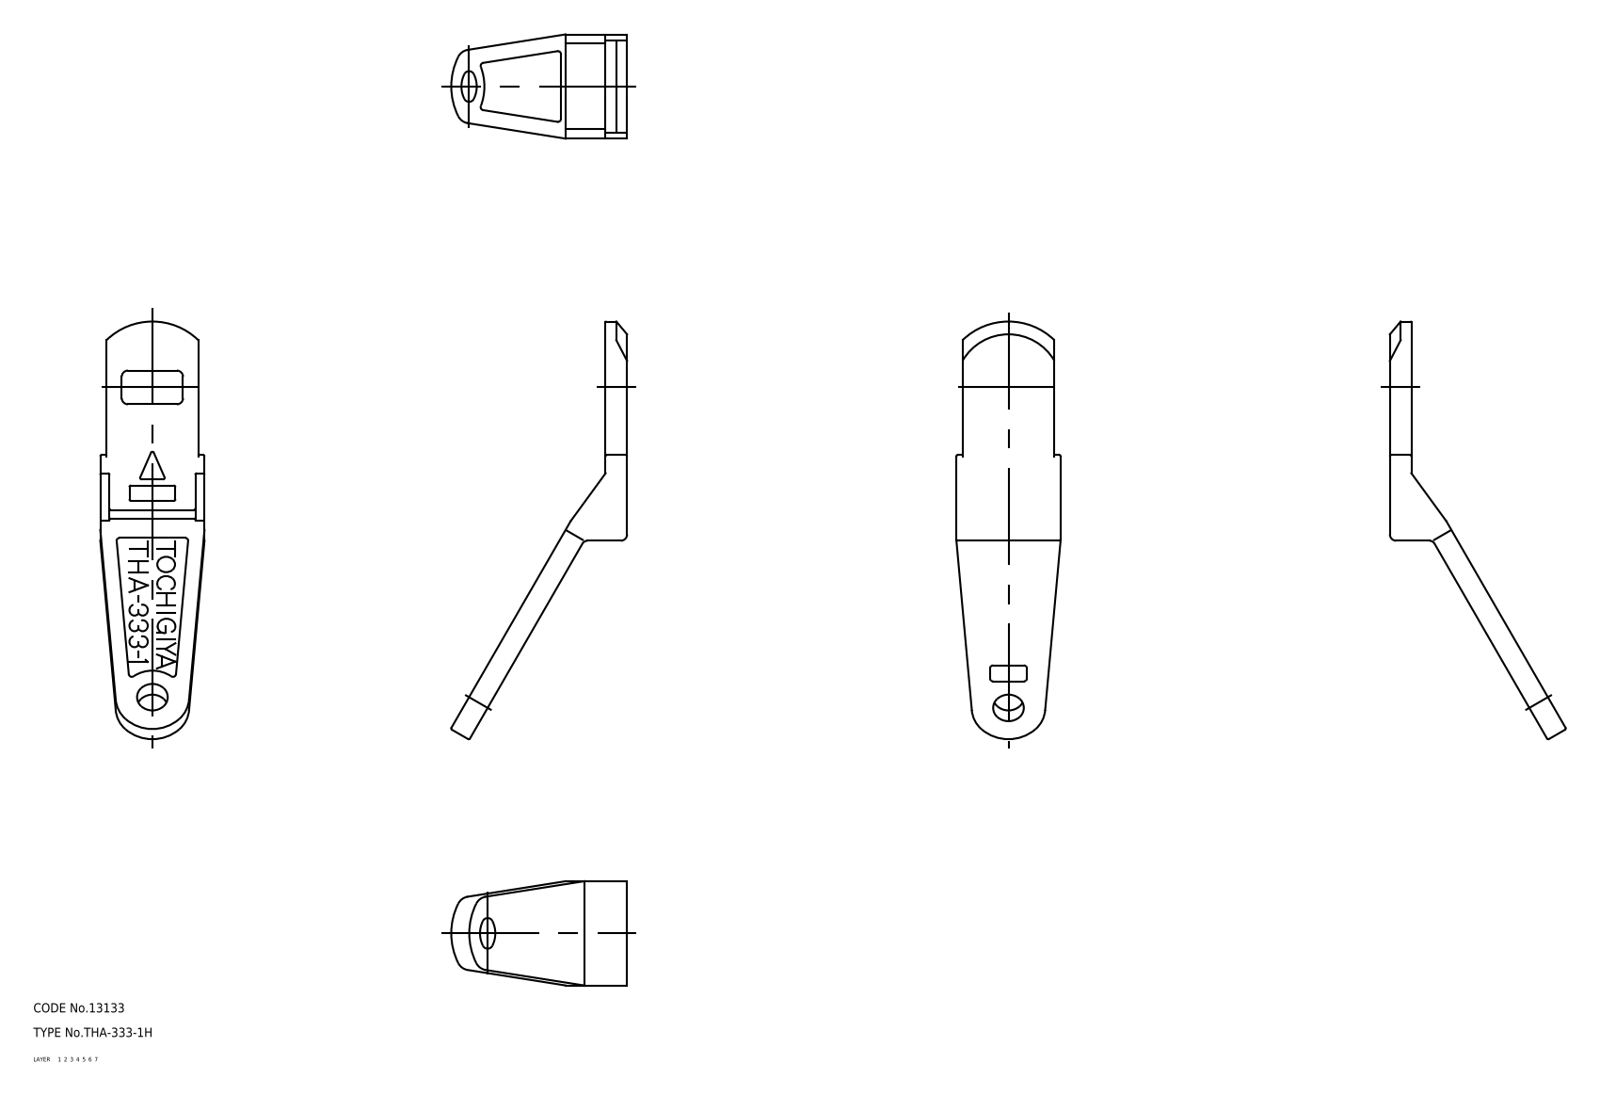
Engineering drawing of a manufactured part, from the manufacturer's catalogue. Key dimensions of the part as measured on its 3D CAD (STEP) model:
Part name (STEP PRODUCT): key_handle
STEP written by: CADfix (AUTOMOTIVE_DESIGN)
Units: millimetres
Bodies: 1 solid, 71 faces (0 planar, 0 cylindrical, 71 other)
Overall size (bounding box): 136.27 × 57.38 × 34
Volume: 31 884 mm³ · Surface area: 11 893 mm²
